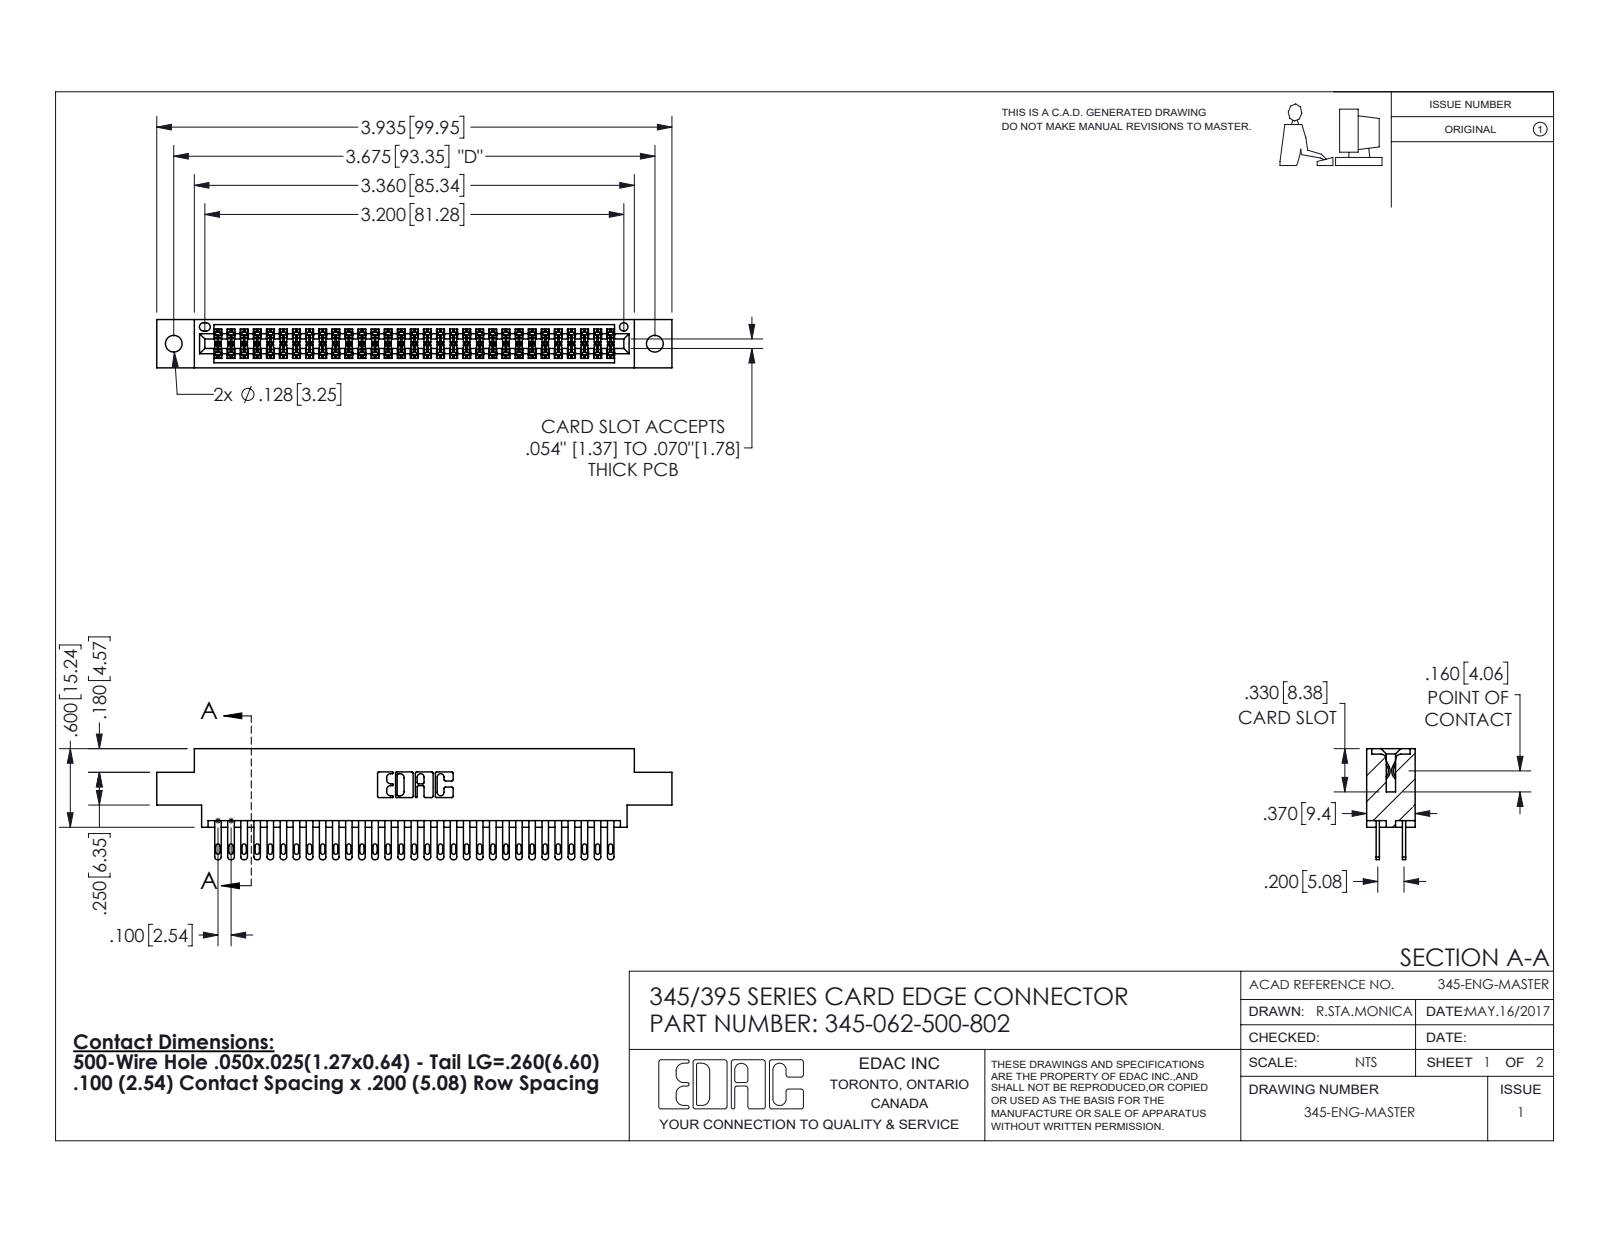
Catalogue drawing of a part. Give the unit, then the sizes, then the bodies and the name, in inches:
Units: inches
Overall size (bounding box): 3.935 × 0.847 × 0.37
Round holes (diameter × count): ⌀0.128 ×2, ⌀0.064 ×1
Partial cylindrical surfaces — rounded edges, fillets, slot ends (radius × count): R0.006 ×93, R0.016 ×62, R0.02 ×62, R0.01 ×22, R0.007 ×6, R0.031 ×6, R0.026 ×3, R0.014 ×2
Main face-to-face distances: 0.298, 0.072, 0.2, 0.098, 0.272, 0.025, 0.37, 0.225, 0.175, 0.149
Hole centre spacings: 0.27, 3.44, 3.675
Volume: 0.589 in³ · Surface area: 22.55 in²
Bodies: 63 solids, 2982 faces (1758 planar, 1224 cylindrical, 0 other)
Part name (STEP PRODUCT): 345 Part_0.170 Offset - 0.128 Dia; 345-292-001_345-293-100; 345-062-500-802
STEP written by: SolidWorks 2016 (CONFIG_CONTROL_DESIGN)
